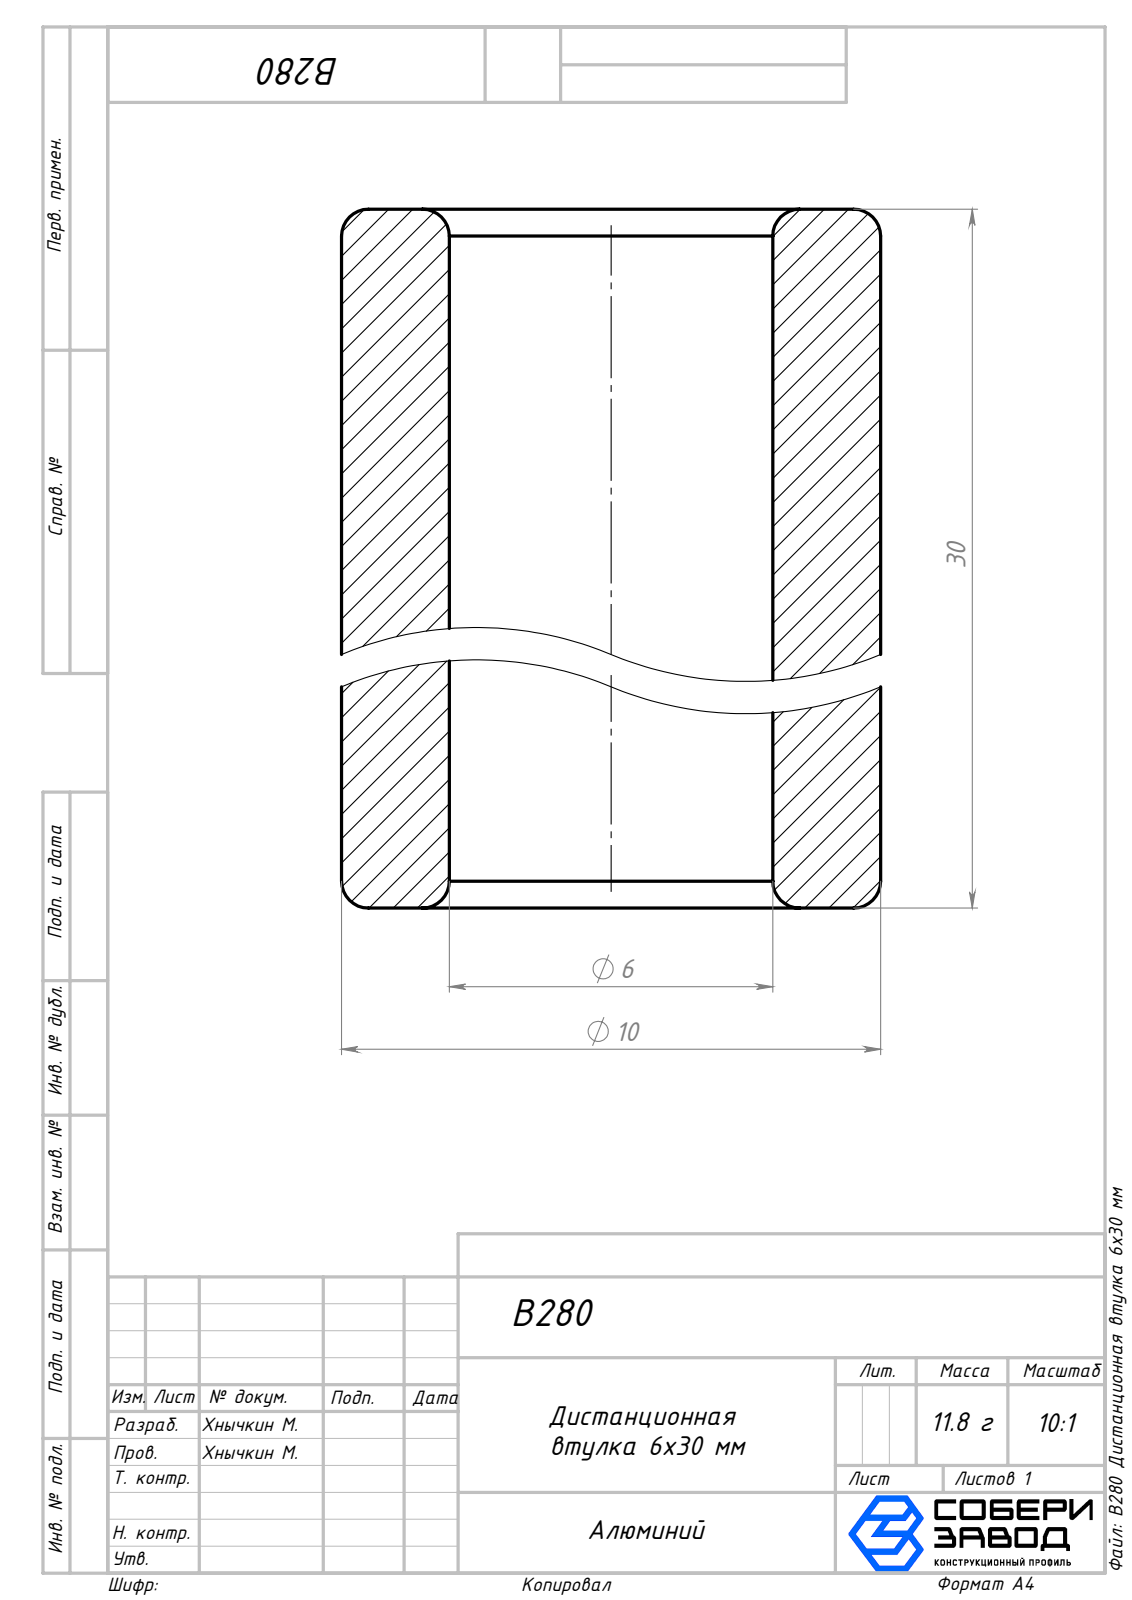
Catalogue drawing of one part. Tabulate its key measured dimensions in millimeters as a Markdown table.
| quantity | value |
| --- | --- |
| part name | B280 Дистанционная втулка 6x30 мм |
| STEP written by | SolidWorks 2026 (AUTOMOTIVE_DESIGN) |
| units | millimeters |
| bodies | 1 solid, 14 faces (2 planar, 4 cylindrical, 8 other) |
| overall size | 30 × 10 × 10 |
| volume | 1 503 mm³ |
| surface area | 1 587 mm² |
| round holes (diameter × count) | 6 × 1 |
| round bosses / shafts (diameter × count) | 10 × 1 |
| main face-to-face distances | 30 |
